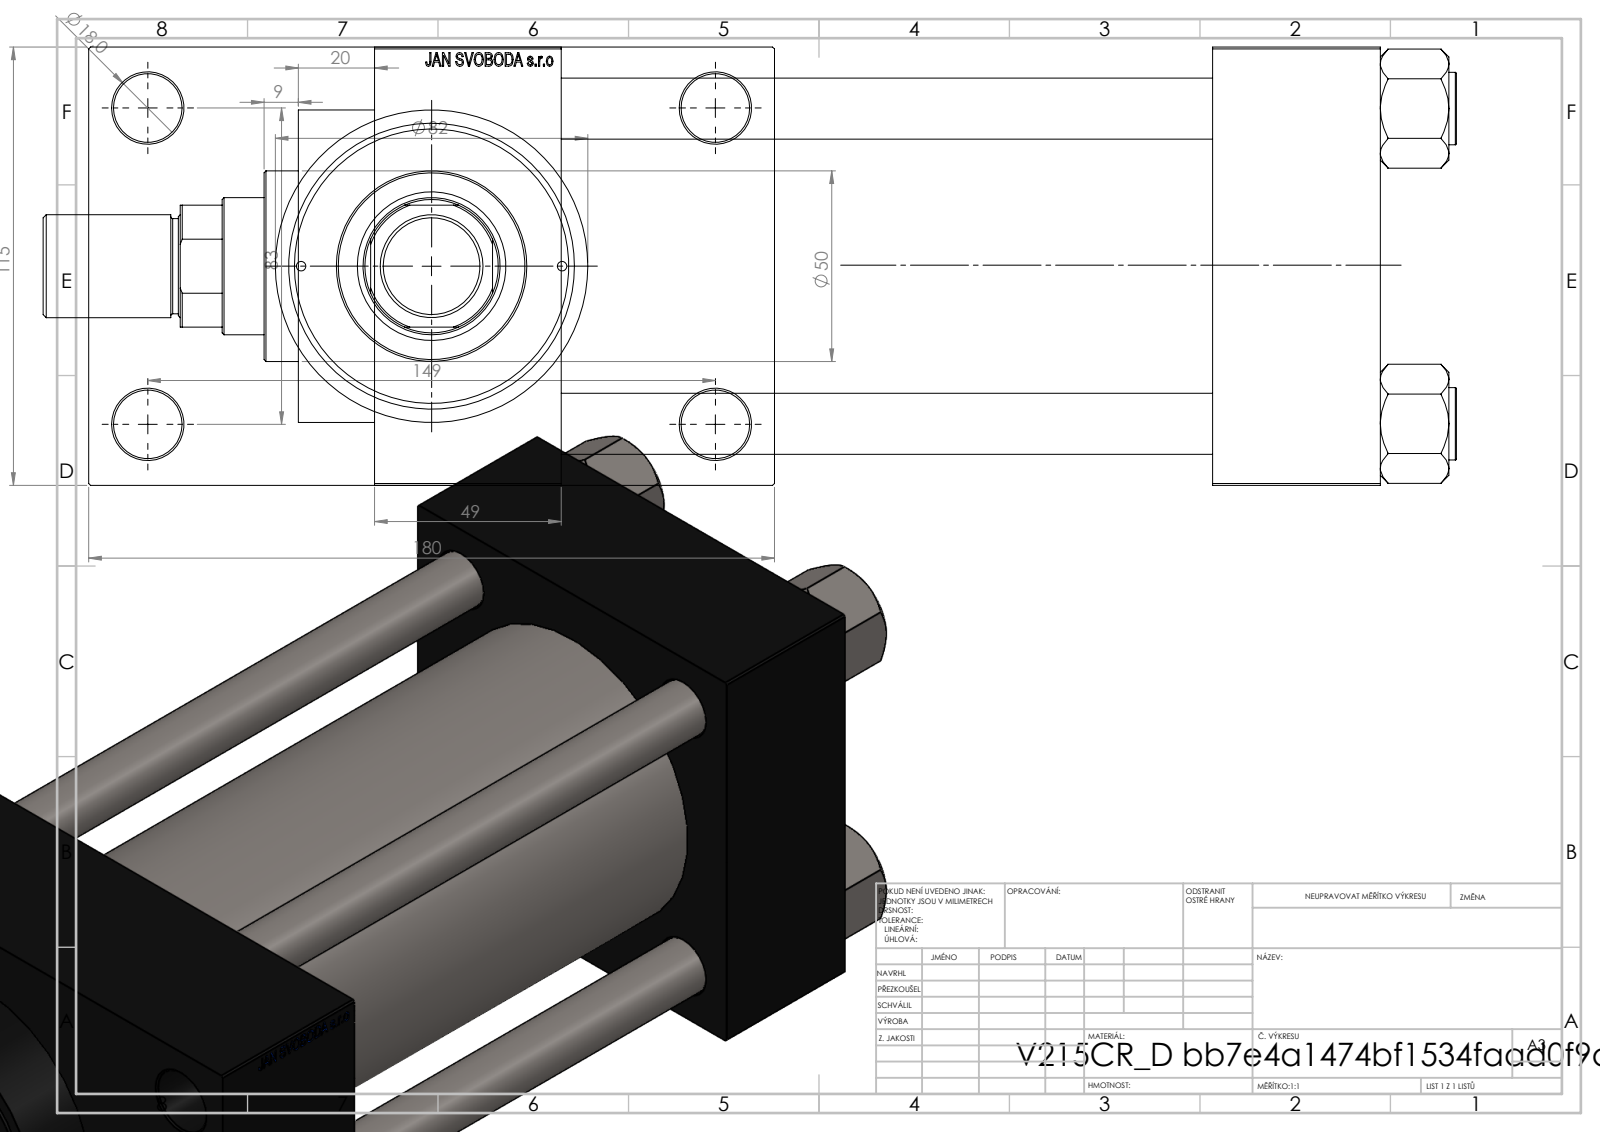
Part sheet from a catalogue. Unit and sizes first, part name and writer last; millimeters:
Units: millimetres
Overall size (bounding box): 371 × 180 × 115
Round holes (diameter × count): ⌀16 ×4, ⌀18 ×4, ⌀2.5 ×2, ⌀7 ×2, ⌀26.44 ×2, ⌀35 ×2, ⌀25.5 ×1, ⌀36 ×1, ⌀39 ×1, ⌀61 ×1, ⌀72 ×1, ⌀80 ×1
Round bosses / shafts (diameter × count): ⌀19 ×4, ⌀86 ×1, ⌀82 ×1, ⌀50 ×1, ⌀27 ×1, ⌀25 ×1
Partial cylindrical surfaces — rounded edges, fillets, slot ends (radius × count): R17.5 ×1
Main face-to-face distances: 115, 171, 220, 49, 44, 215, 264, 32.5, 147.5, 180
Hole centre spacings: 33.15, 41.96, 57.81, 58.48, 82.7, 85.28, 86.17, 89.24
Volume: 2 273 000 mm³ · Surface area: 388 489 mm²
Bodies: 12 solids, 1173 faces (551 planar, 96 cylindrical, 526 other)
Part name (STEP PRODUCT): NUT_M5_D; V215CR_D_TYCINKA; V215CR_D_Body; V215_VC_A (+2 more)
STEP written by: SolidWorks 2019 (CONFIG_CONTROL_DESIGN)
